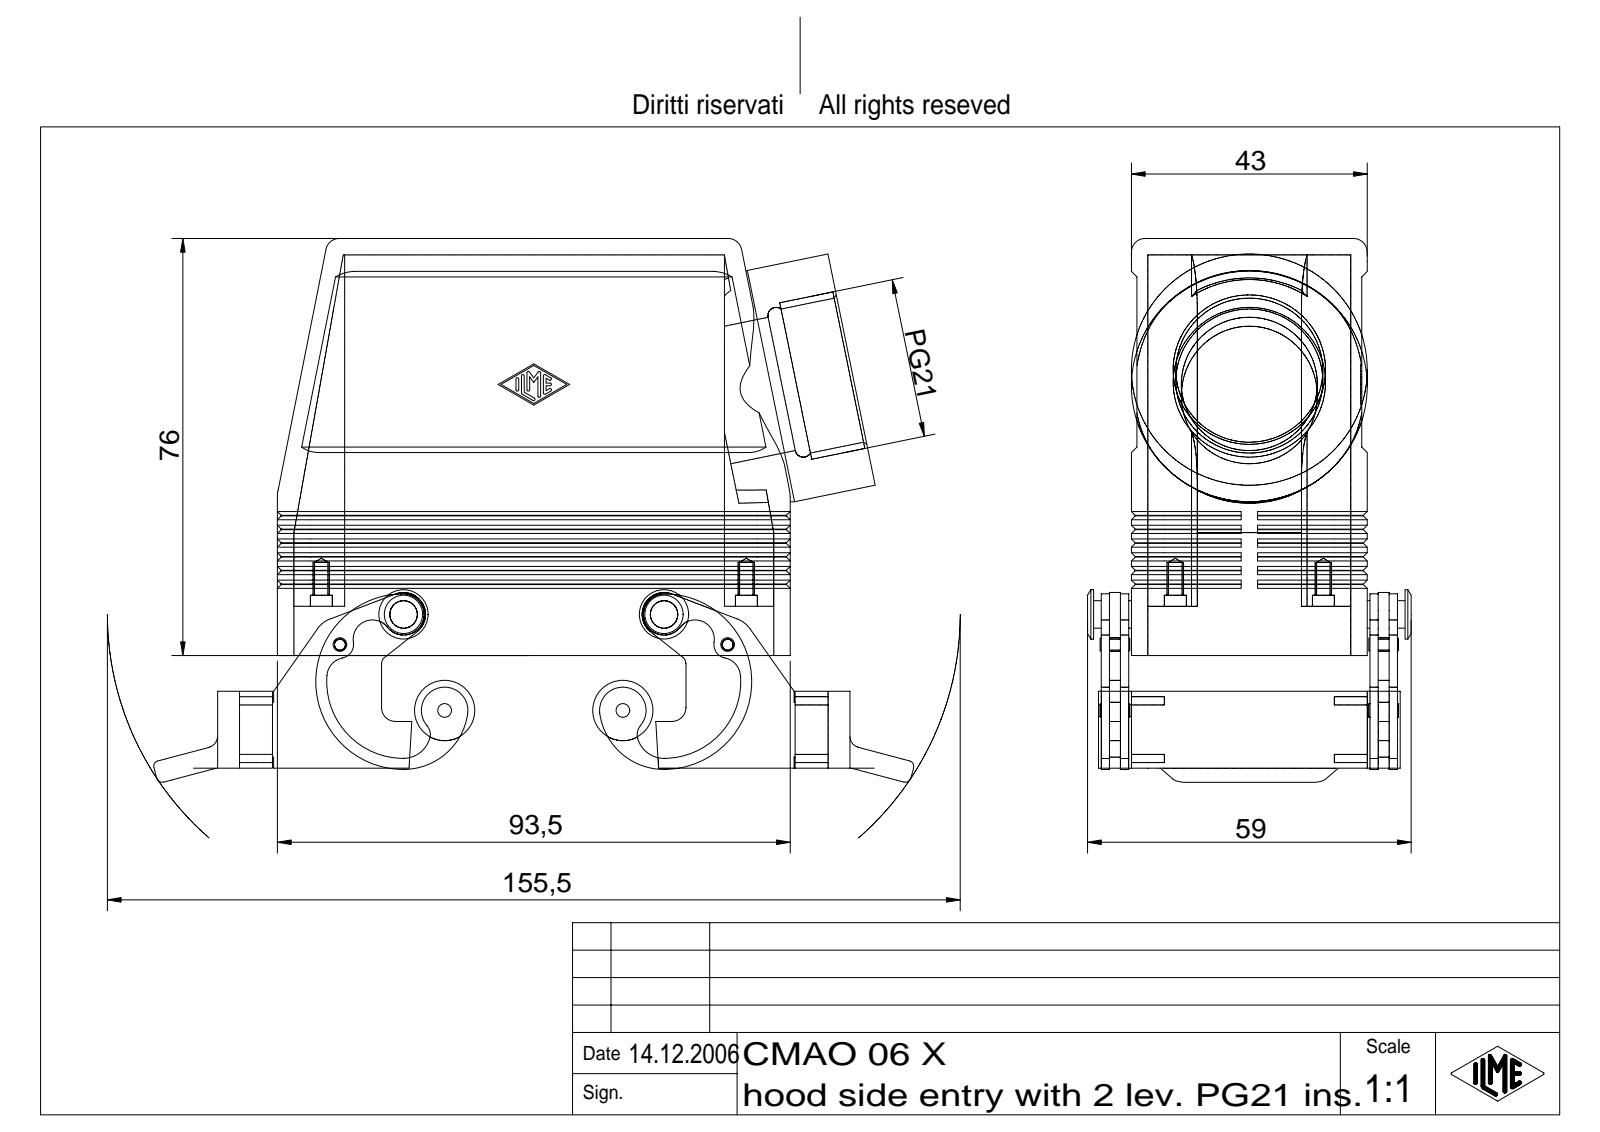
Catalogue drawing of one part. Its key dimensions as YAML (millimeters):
part_name: "CAO Tüllengehäuse 2 Bügel für einen Einsatz"
step_written_by: "Autodesk Inventor 7 (AUTOMOTIVE_DESIGN)"
units: millimeters
bodies: {solids: 1, faces: 956, planar: 283, cylindrical: 254, other: 419}
overall_size: [138.59, 99.1, 59]
volume: 104995
surface_area: 63316
round_holes:
  - {diameter: 2.5, count: 2}
  - {diameter: 24.78, count: 1}
  - {diameter: 26.78, count: 1}
round_bosses_or_shafts:
  - {diameter: 11, count: 2}
  - {diameter: 9, count: 2}
  - {diameter: 5, count: 2}
  - {diameter: 2, count: 2}
  - {diameter: 43, count: 1}
partial_cylinders:
  - {radius: 0.25, count: 14}
  - {radius: 1, count: 12}
  - {radius: 2, count: 10}
  - {radius: 2.5, count: 10}
  - {radius: 6, count: 10}
  - {radius: 3, count: 8}
  - {radius: 3.5, count: 4}
  - {radius: 5, count: 4}
face_to_face_distances: [3, 2, 42, 37, 40, 1, 39, 43, 5, 41]
hole_center_spacings: [70.7]
